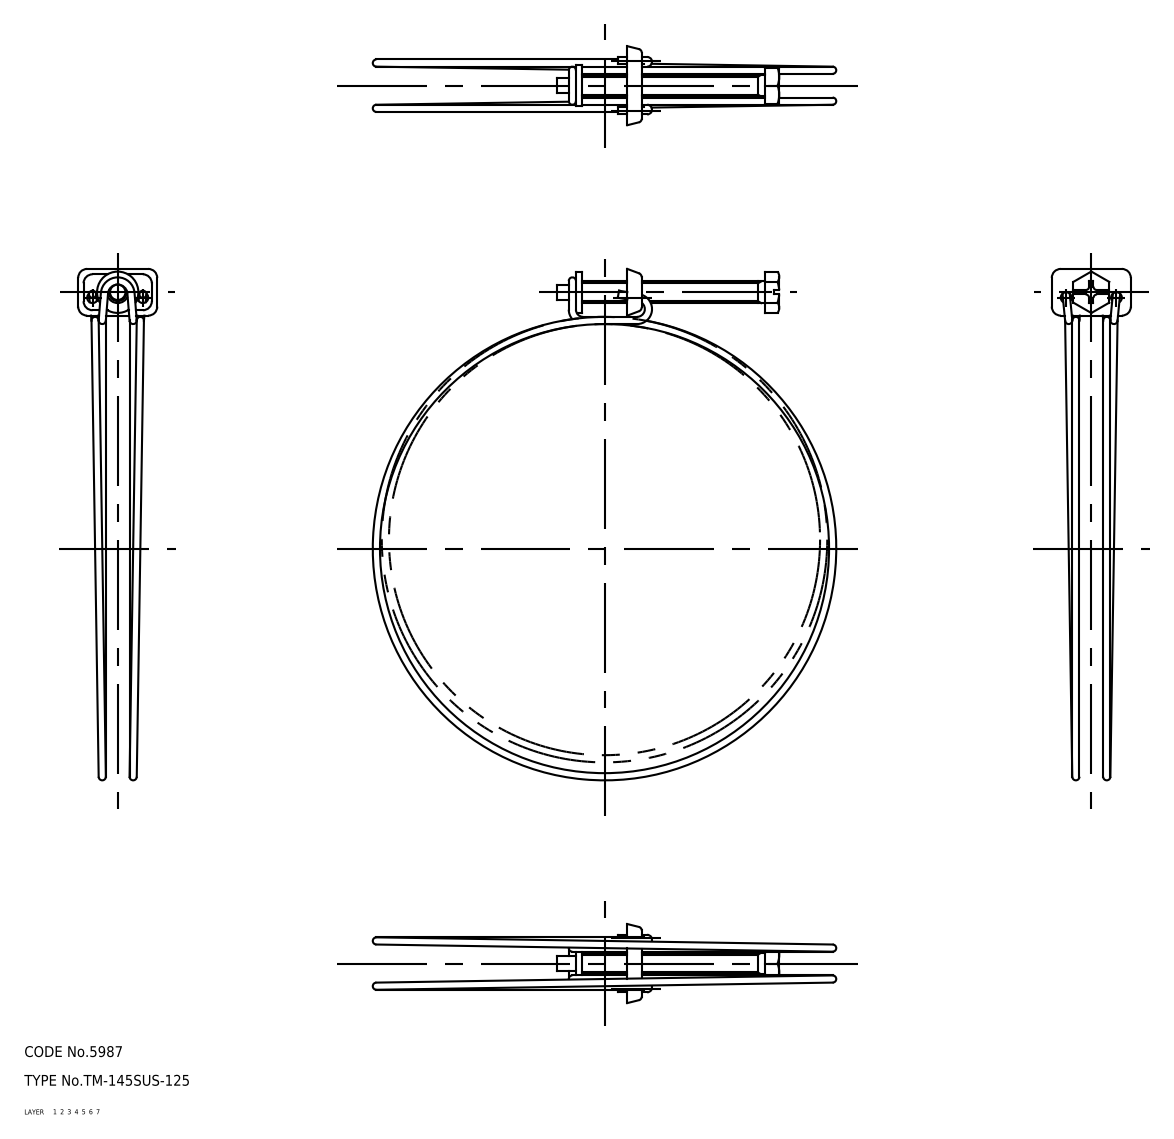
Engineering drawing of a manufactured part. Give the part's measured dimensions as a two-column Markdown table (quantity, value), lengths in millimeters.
| quantity | value |
| --- | --- |
| part name | screw; holder; band; TM_145SUS_125_21315_36 |
| STEP written by | CADfix (AUTOMOTIVE_DESIGN) |
| units | millimeters |
| bodies | 3 solids, 119 faces (0 planar, 0 cylindrical, 119 other) |
| overall size | 142.35 × 129 × 22 |
| volume | 5 291 mm³ |
| surface area | 7 985 mm² |
